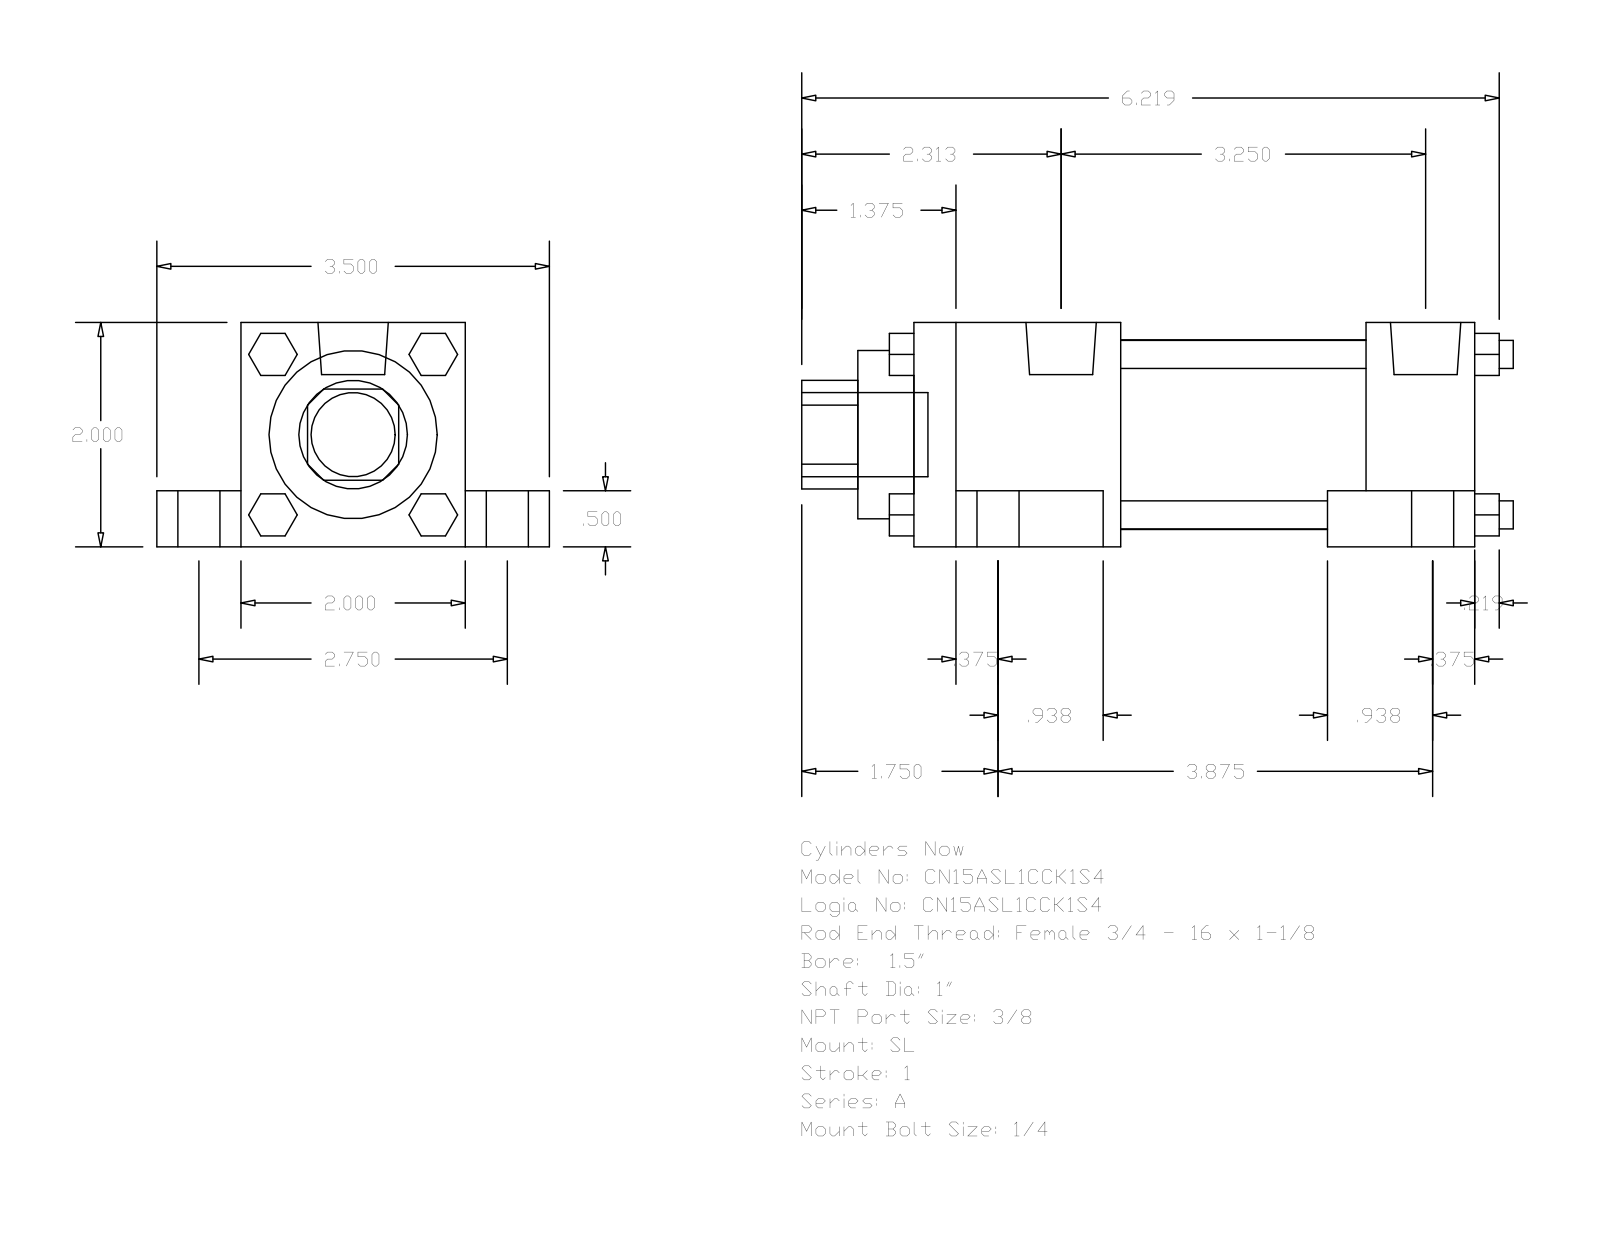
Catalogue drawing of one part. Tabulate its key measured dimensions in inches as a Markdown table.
| quantity | value |
| --- | --- |
| part name | A_SL__0150_1 |
| STEP written by | GSSL Pune (CONFIG_CONTROL_DESIGN) |
| units | inches |
| bodies | 0 solids, 148 faces (112 planar, 36 cylindrical, 0 other) |
| overall size | 6.344 × 3.5 × 2 |
| round holes (diameter × count) | 1 × 1, 1.5 × 1, 1.69 × 1 |
| round bosses / shafts (diameter × count) | 0.625 × 4, 0.375 × 4, 0.25 × 4, 0.219 × 4, 0.627 × 2, 0.75 × 1 |
| partial cylindrical surfaces (radius × count) | 0.484 × 1 |
| main face-to-face distances | 2, 0.5, 1.5, 0.75, 2.75, 2.187, 1.844, 0.375, 5, 2.344 |
